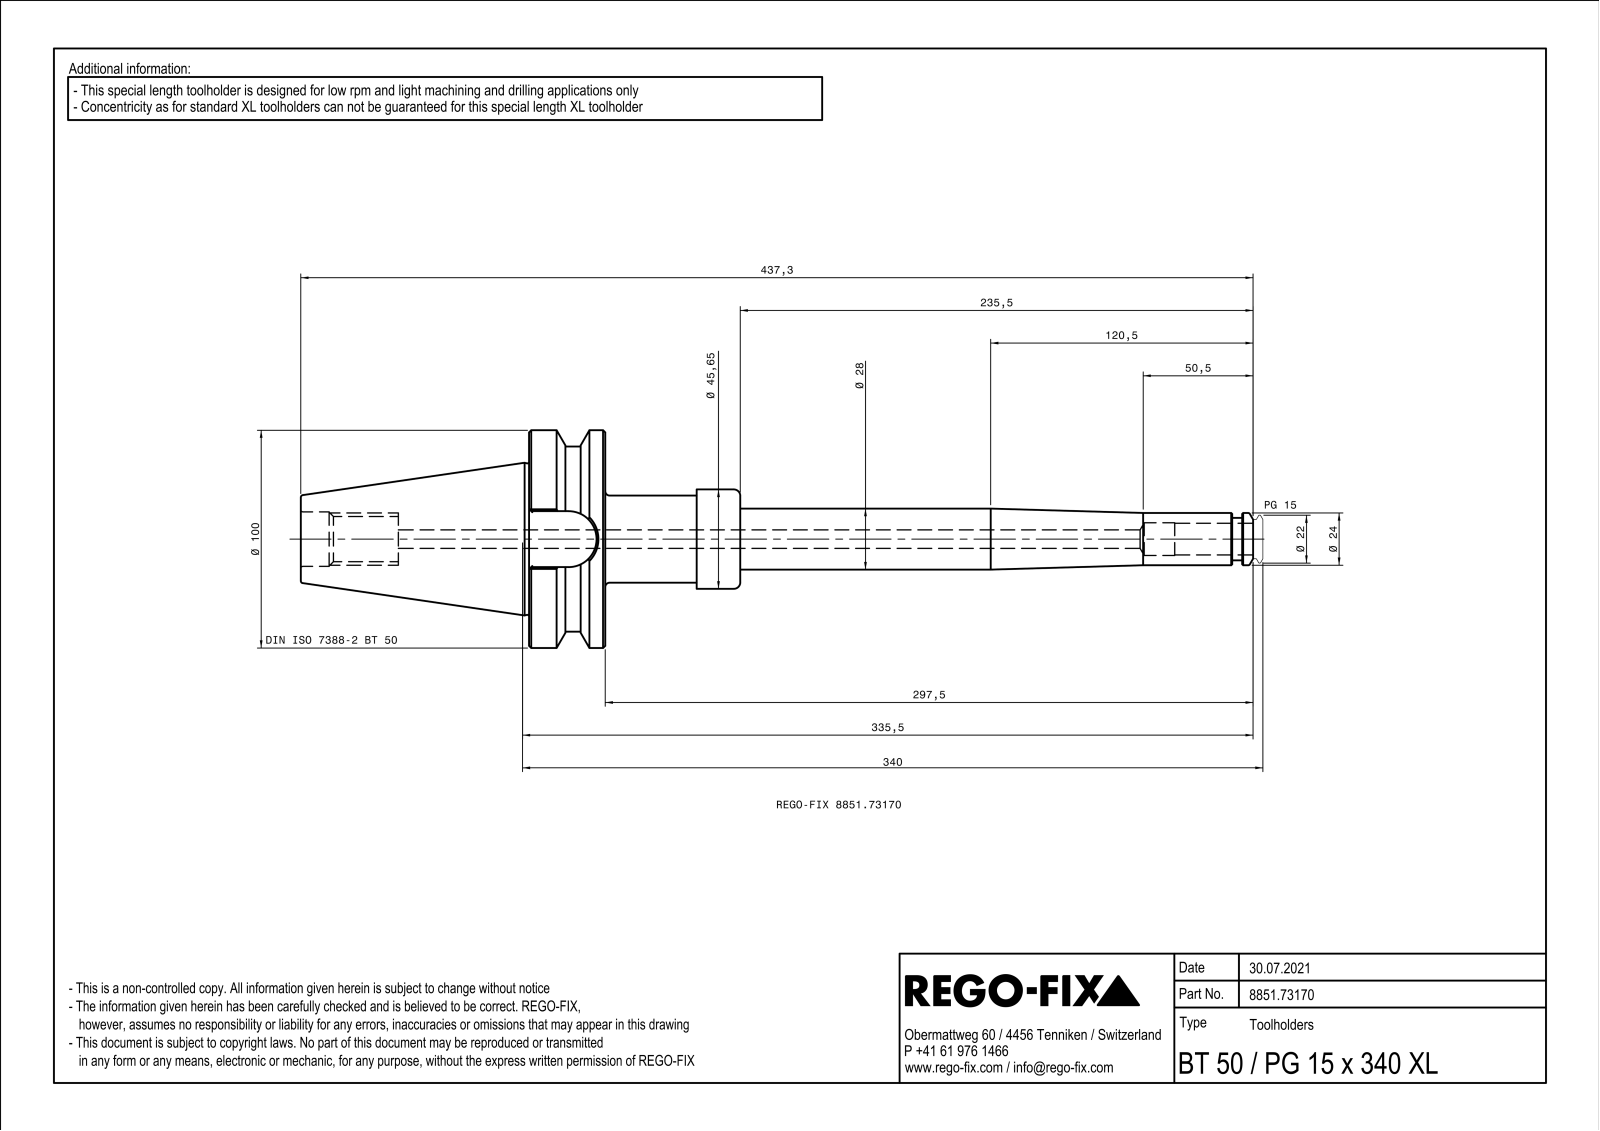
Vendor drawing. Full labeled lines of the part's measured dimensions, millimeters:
Part name (STEP PRODUCT): NOCUT
STEP written by: SIEMENS PLM Software Solid Edge ST10 (AUTOMOTIVE_DESIGN)
Units: millimetres
Bodies: 1 solid, 139 faces (44 planar, 34 cylindrical, 61 other)
Overall size (bounding box): 437.3 × 100 × 100
Volume: 619 572 mm³ · Surface area: 99 554 mm²
Round holes (diameter × count): ⌀9 ×1, ⌀10 ×1, ⌀13 ×1, ⌀15 ×1, ⌀20.75 ×1, ⌀25 ×1, ⌀29 ×1, ⌀38.38 ×1, ⌀40.05 ×1, ⌀43.3 ×1
Round bosses / shafts (diameter × count): ⌀100 ×1, ⌀85 ×1, ⌀45.65 ×1, ⌀40 ×1, ⌀34 ×1, ⌀33 ×1, ⌀28 ×1, ⌀24.7 ×1
Partial cylindrical surfaces — rounded edges, fillets, slot ends (radius × count): R0.5 ×4, R12.85 ×1, R22.77 ×1
Main face-to-face distances: 35, 70.7, 139.8, 104.8, 38.5, 62, 97, 201.8, 6, 14
